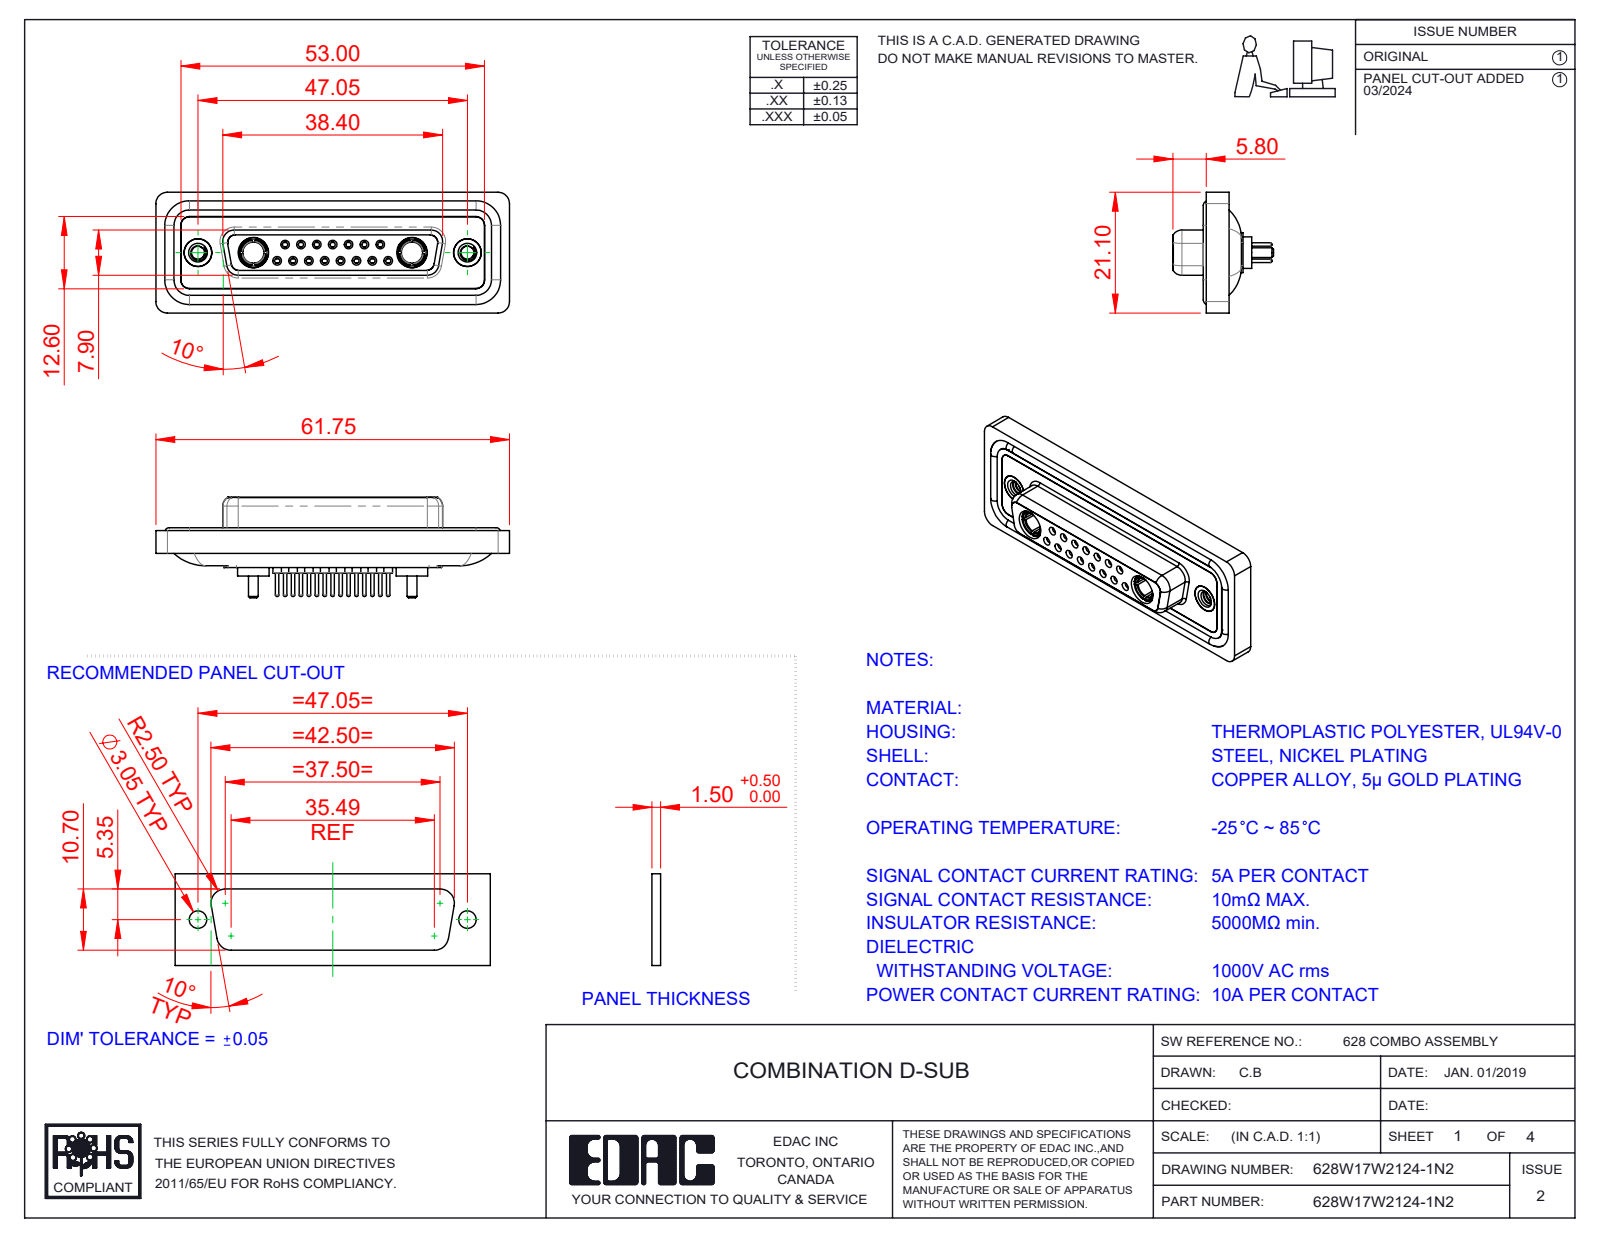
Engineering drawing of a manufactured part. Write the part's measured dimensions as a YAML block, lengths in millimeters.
part_name: "628Combo Housing_17W2; 628Combo Shell Front_25 Contacts; 628Combo Contact Row 2_24; 628Combo Contact Row 1_24 (+5 more)"
step_written_by: "SolidWorks 2023 (CONFIG_CONTROL_DESIGN)"
units: millimeters
bodies: {solids: 26, faces: 1359, planar: 388, cylindrical: 519, other: 452}
overall_size: [61.75, 21.1, 17.55]
volume: 8295
surface_area: 13830
round_holes:
  - {diameter: 0.9, count: 15}
  - {diameter: 1.1, count: 15}
  - {diameter: 1.5, count: 15}
  - {diameter: 2, count: 15}
  - {diameter: 1.6, count: 8}
  - {diameter: 1.7, count: 7}
  - {diameter: 4.85, count: 4}
  - {diameter: 2.26, count: 2}
  - {diameter: 3.7, count: 2}
  - {diameter: 4, count: 2}
  - {diameter: 4.05, count: 2}
  - {diameter: 5, count: 2}
round_bosses_or_shafts:
  - {diameter: 2.2, count: 15}
  - {diameter: 0.6, count: 15}
  - {diameter: 1.6, count: 11}
  - {diameter: 5.5, count: 2}
  - {diameter: 5.2, count: 2}
  - {diameter: 4.96, count: 2}
  - {diameter: 4.95, count: 2}
  - {diameter: 4.8, count: 2}
partial_cylinders:
  - {radius: 1.5, count: 22}
  - {radius: 2, count: 18}
  - {radius: 1.35, count: 8}
  - {radius: 1.6, count: 8}
  - {radius: 0.25, count: 4}
  - {radius: 0.5, count: 4}
  - {radius: 0.6, count: 4}
  - {radius: 0.65, count: 4}
face_to_face_distances: [0.4, 1.8, 7.45, 5.65, 6.6, 0.5, 7.05, 1.6, 2.9, 1.1]
hole_center_spacings: [3.16, 2.77, 8.31, 5.54, 5.03, 5.04, 7.49, 11.08]
